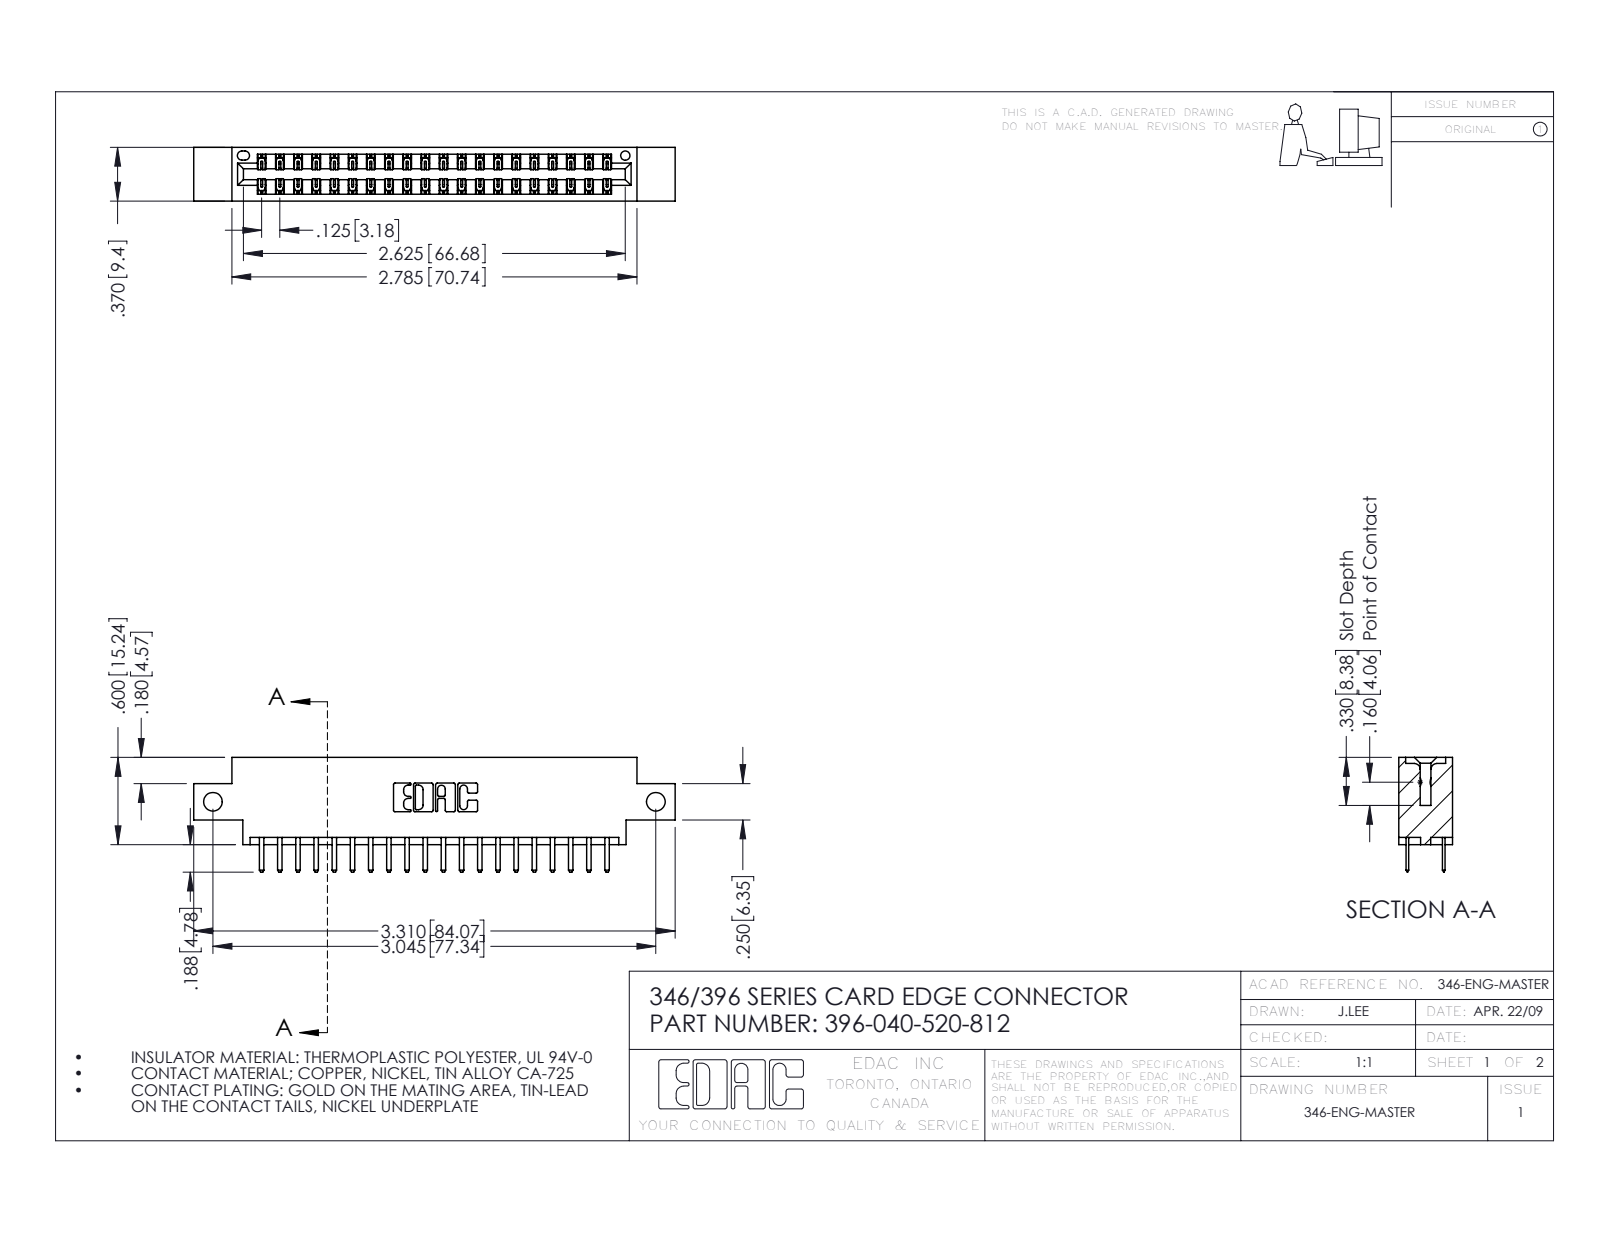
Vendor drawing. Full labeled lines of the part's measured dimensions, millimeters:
Part name (STEP PRODUCT): 346 Part_0.170 Offset - Side Mount; 345-292-001_345-293-120; 396-040-520-812
STEP written by: SolidWorks 2016 (CONFIG_CONTROL_DESIGN)
Units: millimetres
Bodies: 41 solids, 2366 faces (1560 planar, 806 cylindrical, 0 other)
Overall size (bounding box): 84.1 × 20 × 9.4
Volume: 7 770 mm³ · Surface area: 10 340 mm²
Round holes (diameter × count): ⌀3.3 ×2, ⌀1.6 ×1
Partial cylindrical surfaces — rounded edges, fillets, slot ends (radius × count): R0.2 ×60, R0.3 ×44, R0.3 ×22, R0.2 ×6, R0.8 ×6, R0.7 ×3, R0.4 ×2, R0.6 ×2
Main face-to-face distances: 1.2, 8.2, 6.4, 9.4, 7, 1.8, 7.6, 0.6, 3.8, 5.6
Hole centre spacings: 77.3
